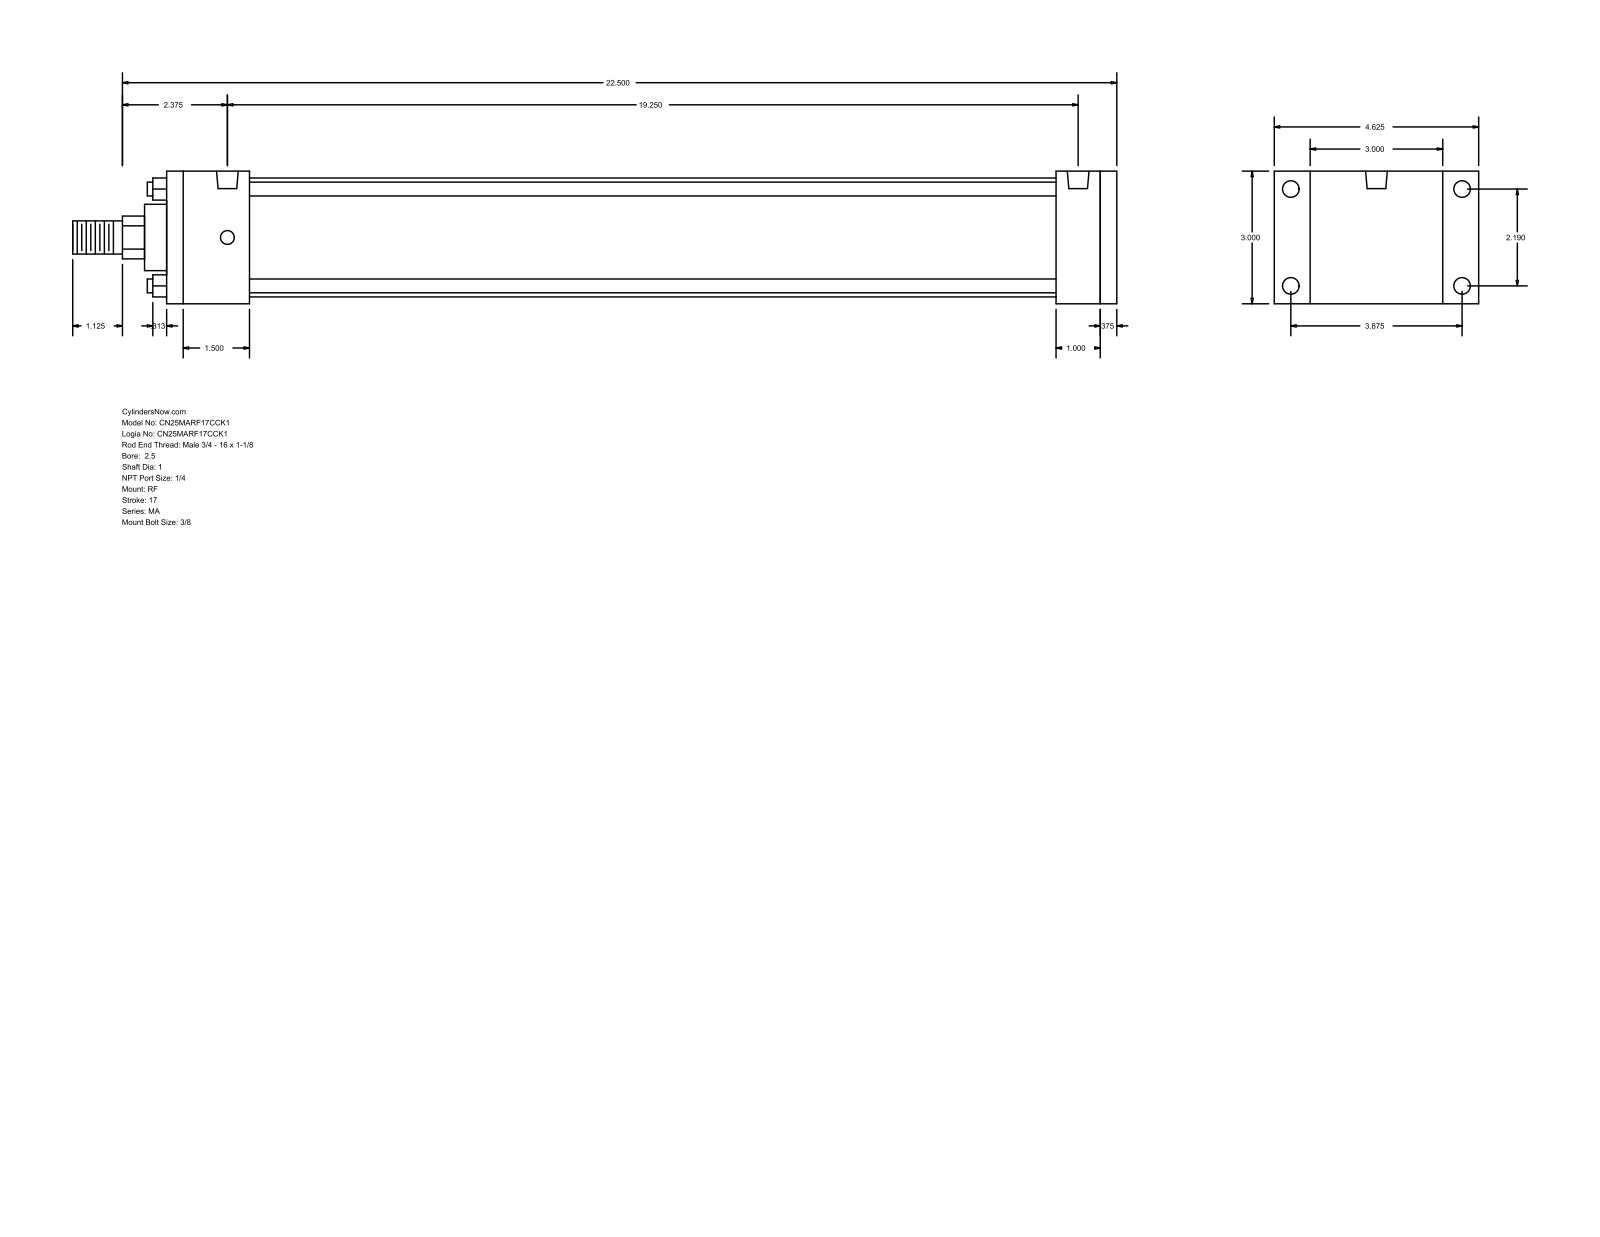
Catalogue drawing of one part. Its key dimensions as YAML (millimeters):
part_name: "MA_RF__0250_1"
step_written_by: "GSSL Pune (CONFIG_CONTROL_DESIGN)"
units: millimeters
bodies: {solids: 0, faces: 92, planar: 64, cylindrical: 28, other: 0}
overall_size: [600.08, 117.47, 76.2]
round_holes:
  - {diameter: 7.94, count: 4}
  - {diameter: 9.53, count: 4}
  - {diameter: 12.49, count: 2}
round_bosses_or_shafts:
  - {diameter: 7.94, count: 4}
  - {diameter: 68.33, count: 1}
  - {diameter: 38.1, count: 1}
  - {diameter: 25.4, count: 1}
  - {diameter: 19.05, count: 1}
partial_cylinders:
  - {radius: 12.29, count: 1}
face_to_face_distances: [76.2, 546.1, 536.58, 9.52, 25.4, 47.63, 511.18, 463.55, 488.95, 498.47]
hole_center_spacings: [55.62, 98.42, 113.05, 488.94]
